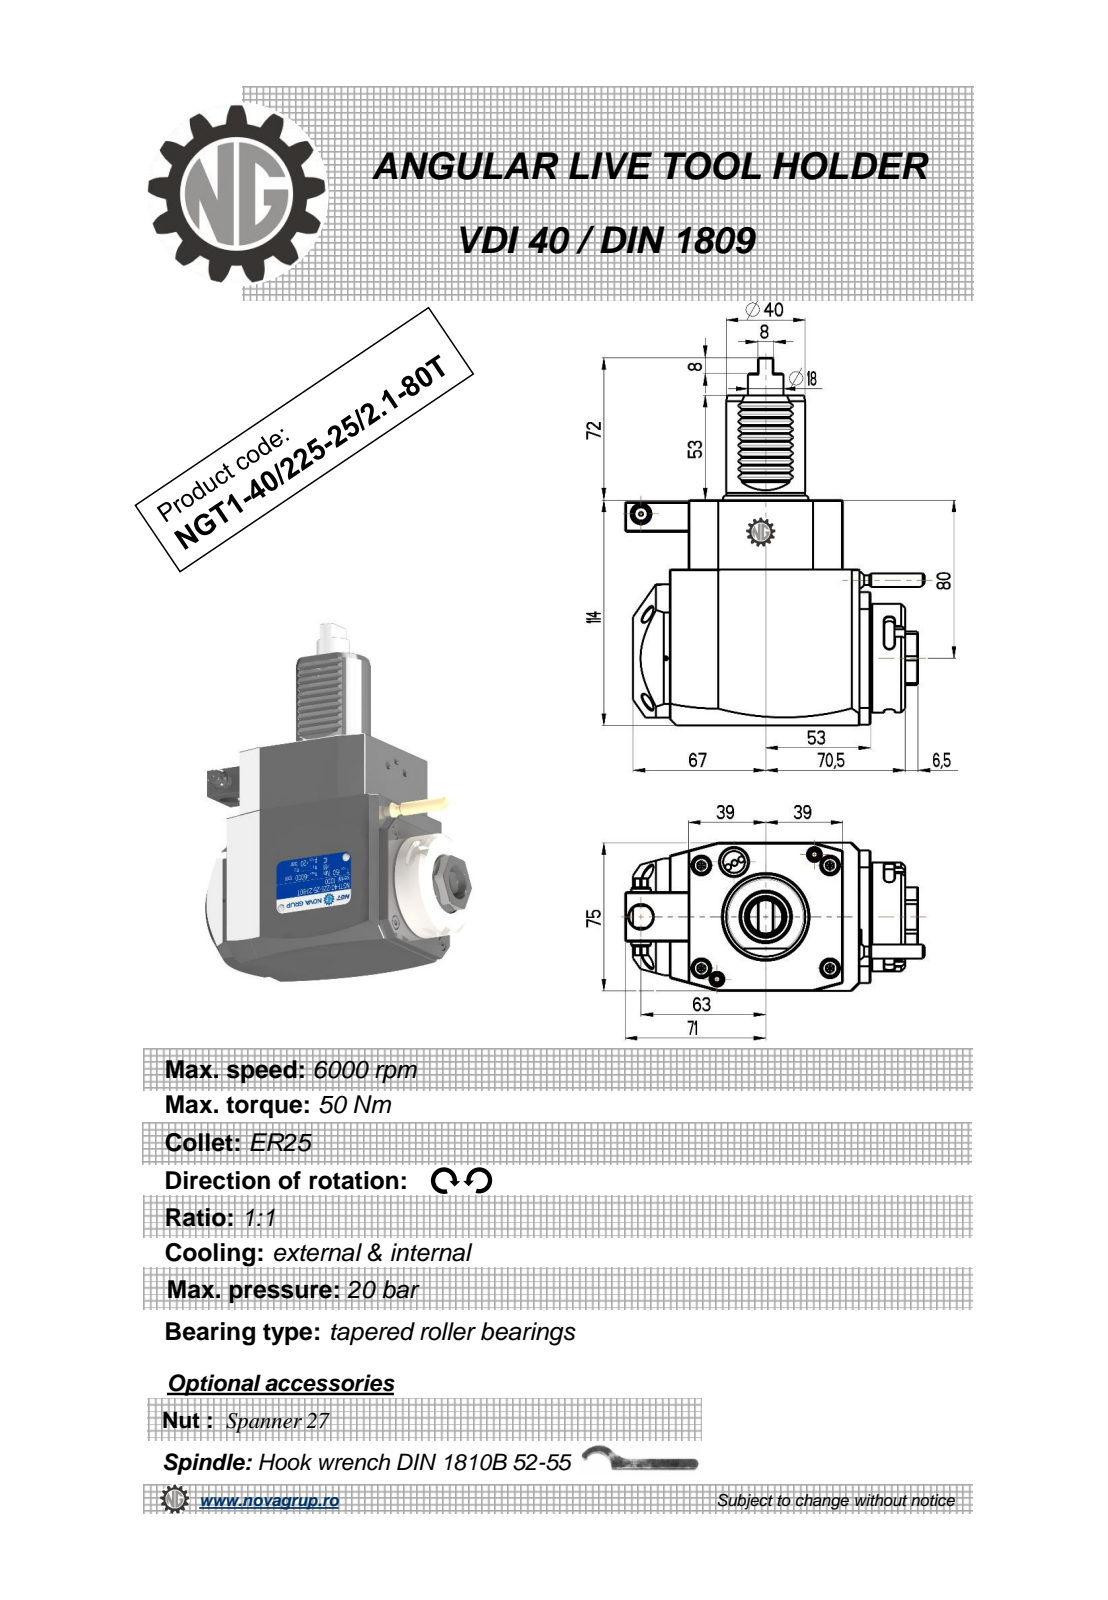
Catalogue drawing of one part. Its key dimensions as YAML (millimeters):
part_name: "NGT1_40_225_25_1_1_80T"
step_written_by: "PRO/ENGINEER BY PARAMETRIC TECHNOLOGY CORPORATION, 2010280 (CONFIG_CONTROL_DESIGN)"
units: millimeters
bodies: {solids: 1, faces: 351, planar: 187, cylindrical: 90, other: 74}
overall_size: [186, 151.33, 75]
volume: 949173
surface_area: 70586
round_holes:
  - {diameter: 2, count: 1}
  - {diameter: 2.5, count: 1}
  - {diameter: 3, count: 1}
  - {diameter: 4.5, count: 1}
  - {diameter: 9.5, count: 1}
  - {diameter: 12, count: 1}
  - {diameter: 18, count: 1}
round_bosses_or_shafts:
  - {diameter: 8, count: 2}
  - {diameter: 55, count: 1}
  - {diameter: 48, count: 1}
  - {diameter: 40, count: 1}
  - {diameter: 17.8, count: 1}
  - {diameter: 10, count: 1}
  - {diameter: 7, count: 1}
  - {diameter: 5, count: 1}
partial_cylinders:
  - {radius: 0.3, count: 10}
  - {radius: 2.5, count: 6}
  - {radius: 0.8, count: 2}
  - {radius: 180, count: 2}
  - {radius: 0.5, count: 1}
  - {radius: 3.85, count: 1}
  - {radius: 4.25, count: 1}
  - {radius: 15, count: 1}
face_to_face_distances: [75, 114, 14, 17.5, 78, 92, 31.5, 109.5, 35, 4]
hole_center_spacings: [37.35, 43.2, 72.5]
